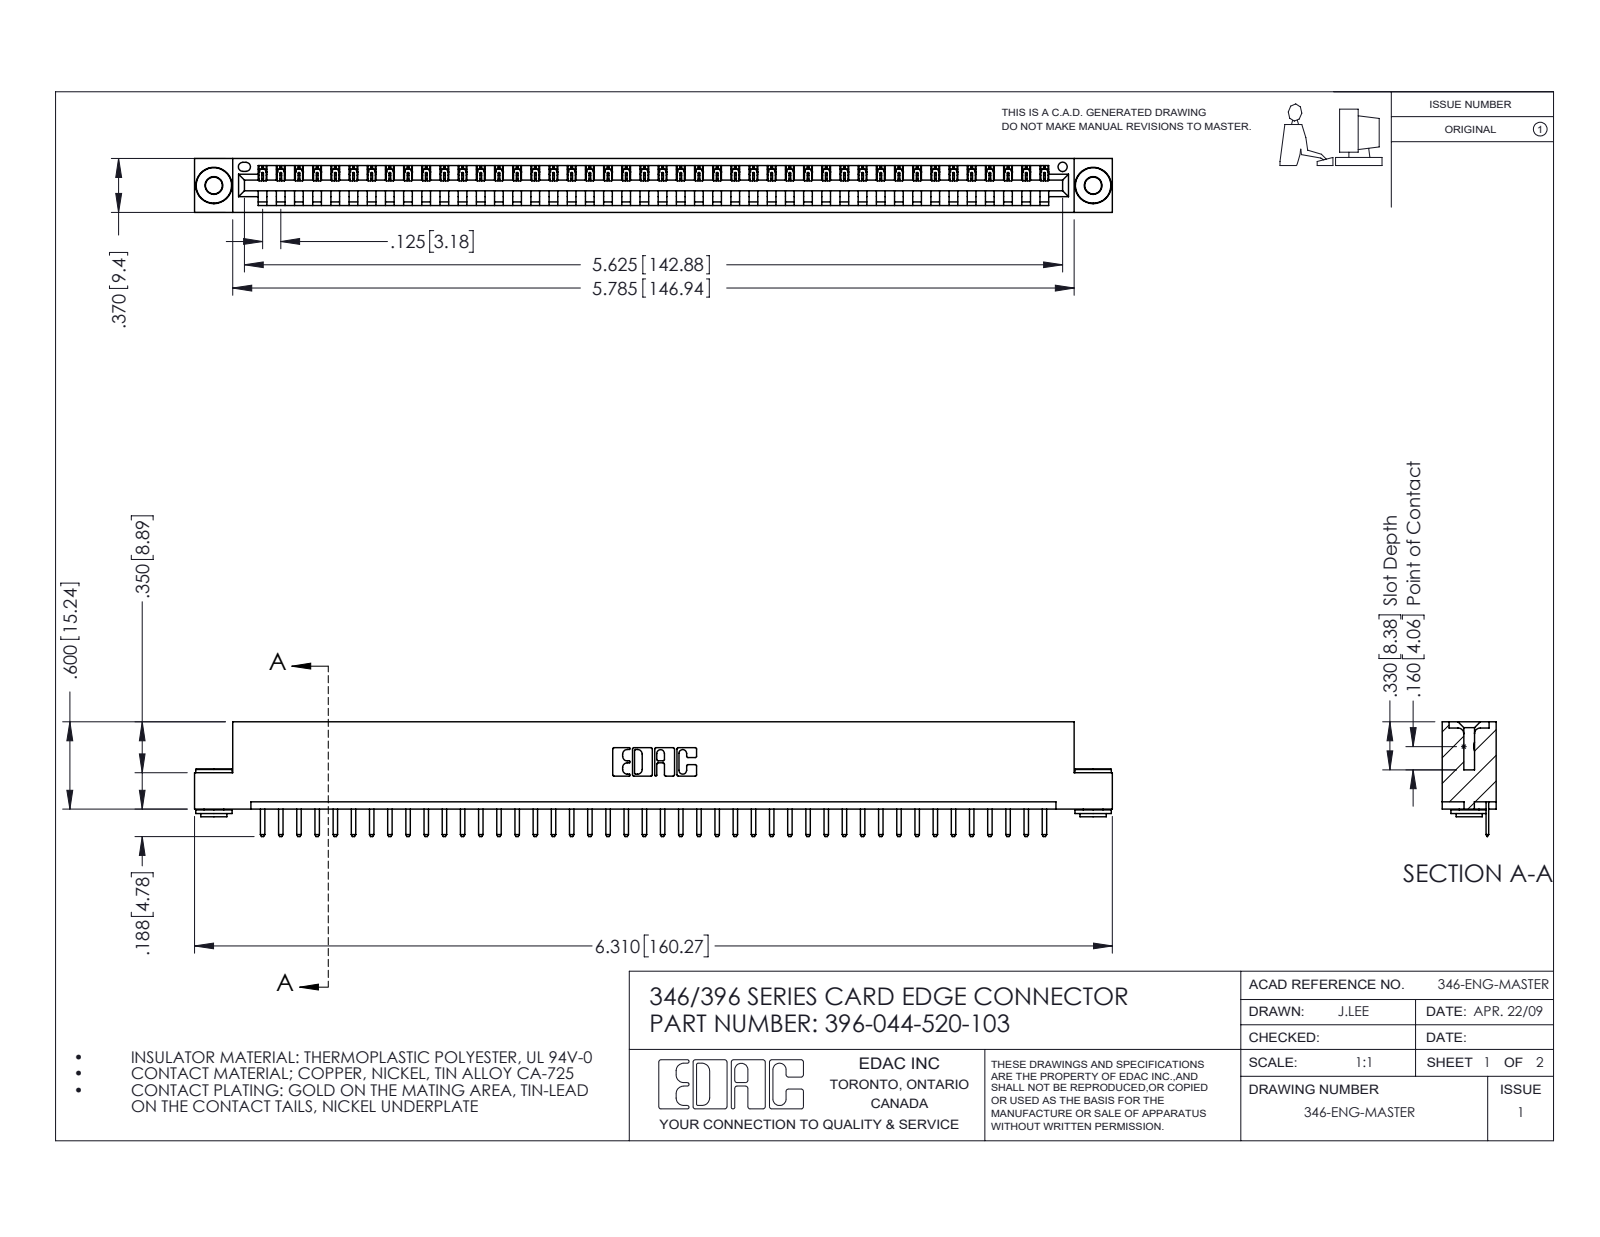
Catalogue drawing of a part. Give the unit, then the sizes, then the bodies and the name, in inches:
Units: inches
Overall size (bounding box): 6.31 × 0.788 × 0.37
Round holes (diameter × count): ⌀0.116 ×2, ⌀0.156 ×2, ⌀0.064 ×1
Round bosses / shafts (diameter × count): ⌀0.25 ×2, ⌀0.18 ×2, ⌀0.136 ×2
Partial cylindrical surfaces — rounded edges, fillets, slot ends (radius × count): R0.01 ×90, R0.006 ×88, R0.01 ×22, R0.007 ×6, R0.031 ×6, R0.026 ×3, R0.031 ×2, R0.04 ×2
Main face-to-face distances: 0.048, 0.322, 0.37, 0.25, 0.148, 0.222, 0.1, 0.174, 0.025, 0.072
Hole centre spacings: 0.246, 5.836, 6.045
Volume: 0.931 in³ · Surface area: 29.26 in²
Bodies: 47 solids, 2888 faces (1934 planar, 946 cylindrical, 8 other)
Part name (STEP PRODUCT): 396-044-520-103; 345-250-002_345-250-002-102; 346 Part_Flush Mounting Lugs - 0.156 Dia-TH; 345-292-001_345-293-120
STEP written by: SolidWorks 2016 (CONFIG_CONTROL_DESIGN)
